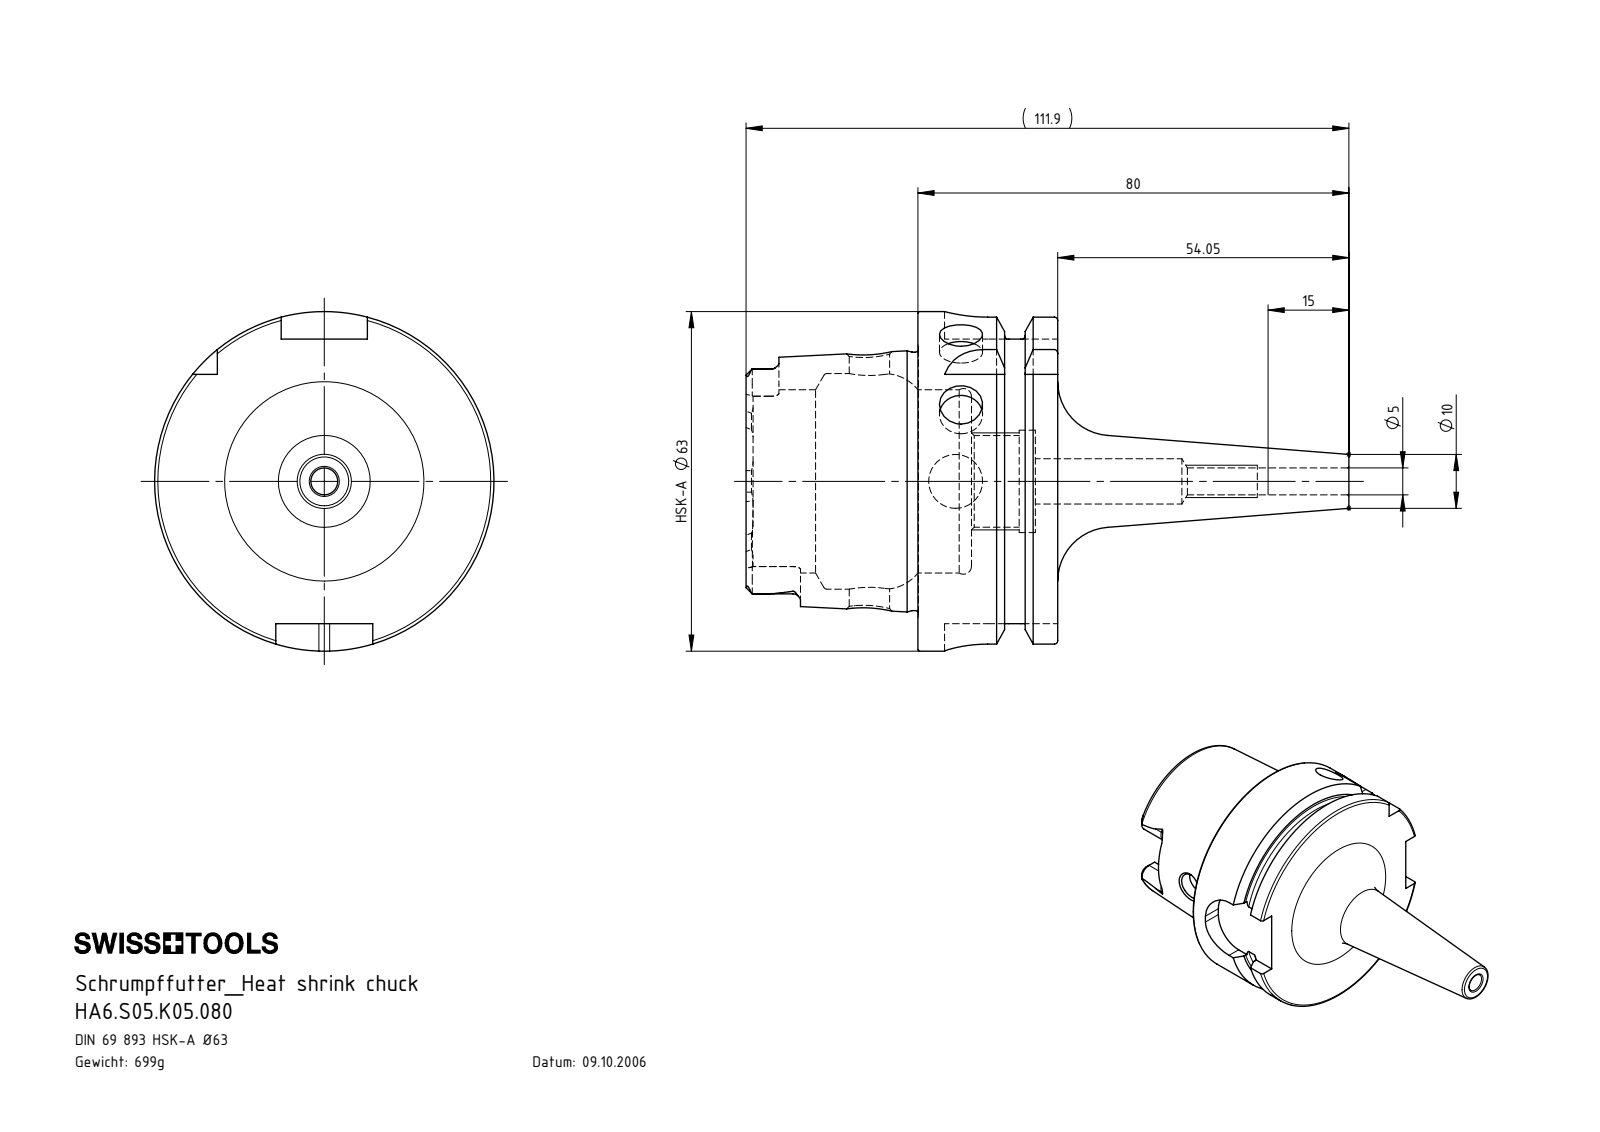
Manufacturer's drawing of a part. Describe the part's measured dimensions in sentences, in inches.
The part is named "HA6.S05.K05.080". Its 3-D file was written by "SolidWorks 2017 (AUTOMOTIVE_DESIGN)". It is 1 solid with 139 faces: 48 planar, 34 cylindrical and 57 other. Overall it measures 4.406 by 2.48 by 2.48 inches. Its volume is 5.432 cubic inches and its surface area 39.76 square inches. Round holes: 2 of diameter 0.315, 1 of diameter 0.197, 1 of diameter 0.217, 1 of diameter 0.295, 1 of diameter 0.331, 1 of diameter 0.394, 1 of diameter 0.669, 1 of diameter 0.748, 1 of diameter 1.339, 1 of diameter 1.575. Round bosses or shafts: 1 of diameter 2.48, 1 of diameter 2.163, 1 of diameter 1.887. Partial cylindrical surfaces (rounded edges, fillets, slot ends): 6 of radius 0.055, 4 of radius 0.113, 4 of radius 0.315. The main face-to-face distances are 1.022, 0.63, 0.392, 1.256, 1.648, 2.278, 2.079, 0.858, 0.467, 2.114.
